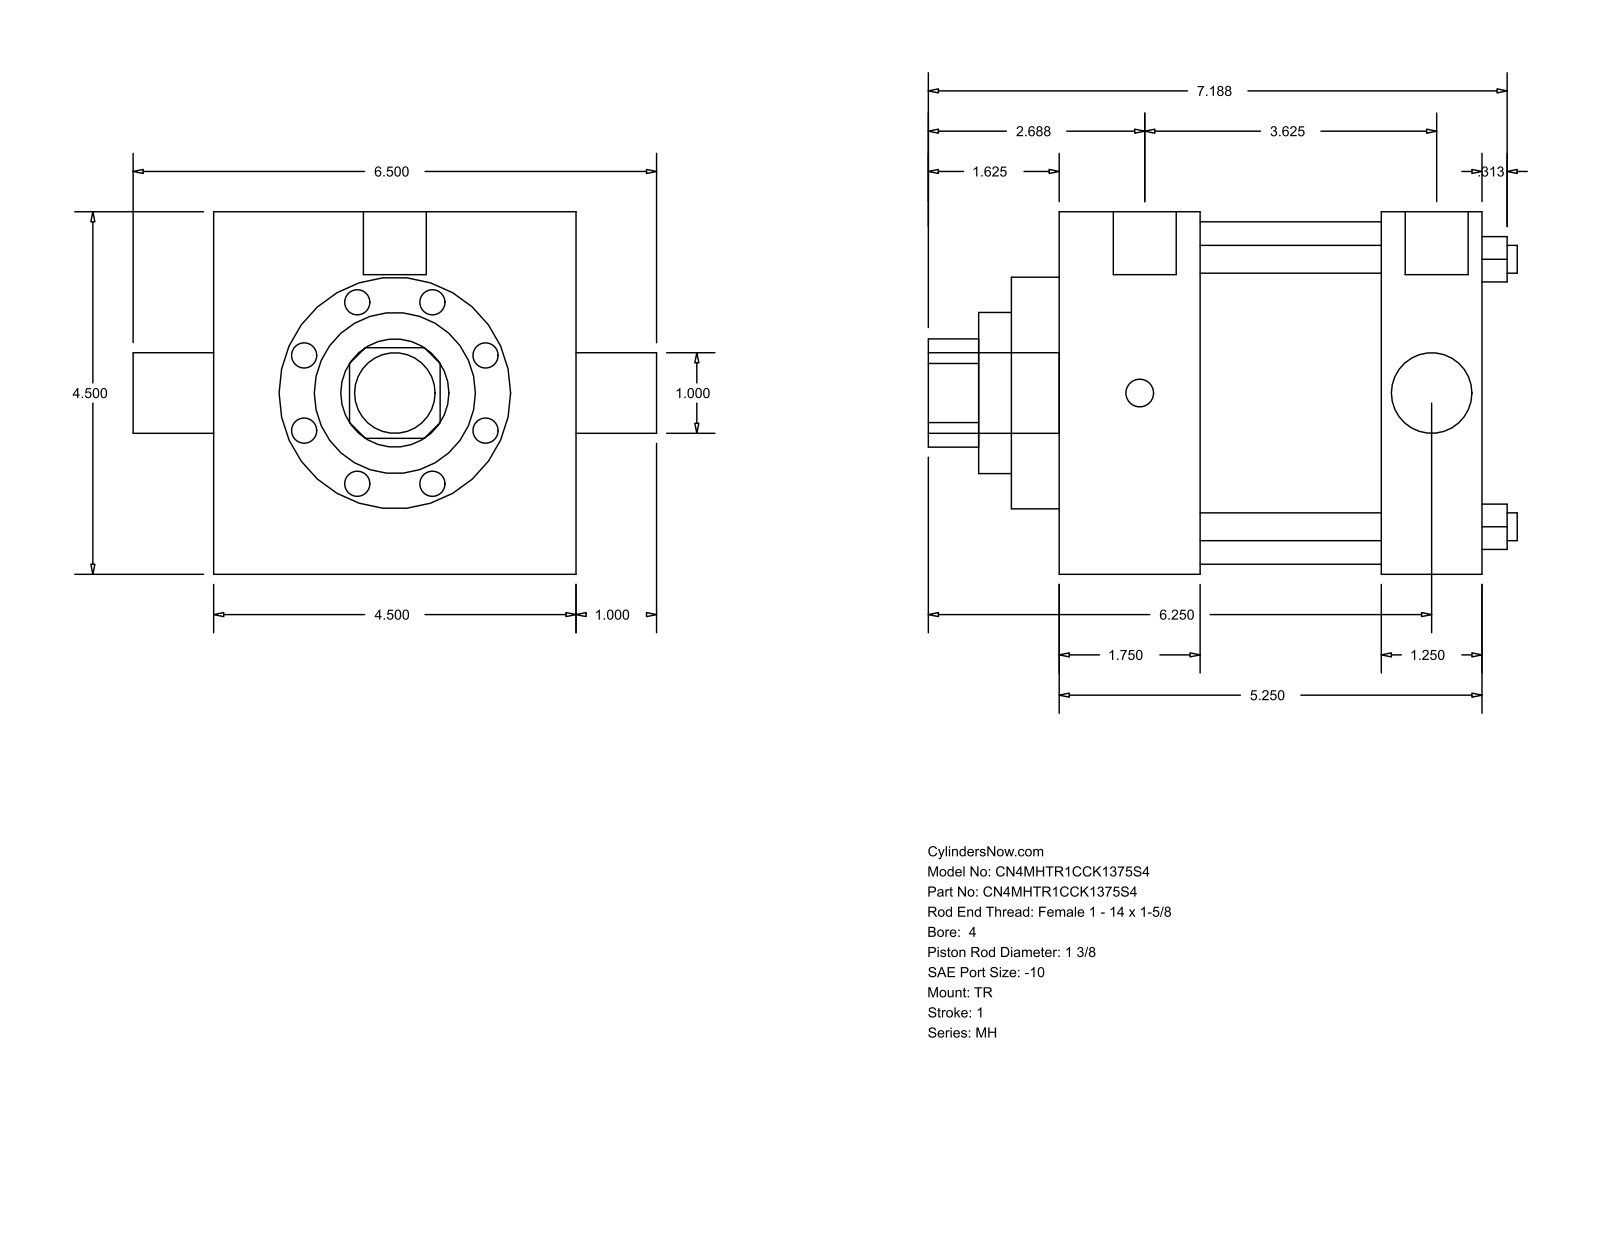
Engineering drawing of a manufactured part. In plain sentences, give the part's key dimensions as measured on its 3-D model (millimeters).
The part is named "MH_TR__0400_1.375". Its 3-D file was written by "GSSL Pune (CONFIG_CONTROL_DESIGN)". It is 0 solids with 86 faces: 61 planar, 25 cylindrical and 0 other. Overall it measures 185.74 by 165.1 by 114.3 millimeters. Round holes: 4 of diameter 8.76, 1 of diameter 25.4, 1 of diameter 34.92, 1 of diameter 50.8, 1 of diameter 73.03, 1 of diameter 107.95. Round bosses or shafts: 3 of diameter 8.73, 2 of diameter 19.84, 1 of diameter 25.4. Partial cylindrical surfaces (rounded edges, fillets, slot ends): 1 of radius 17.06. The main face-to-face distances are 114.3, 133.35, 44.45, 88.9, 101.61, 57.16, 31.74, 15.08, 59.53, 116.69. The hole center spacings are 59.62, 84.32, 119.25.
